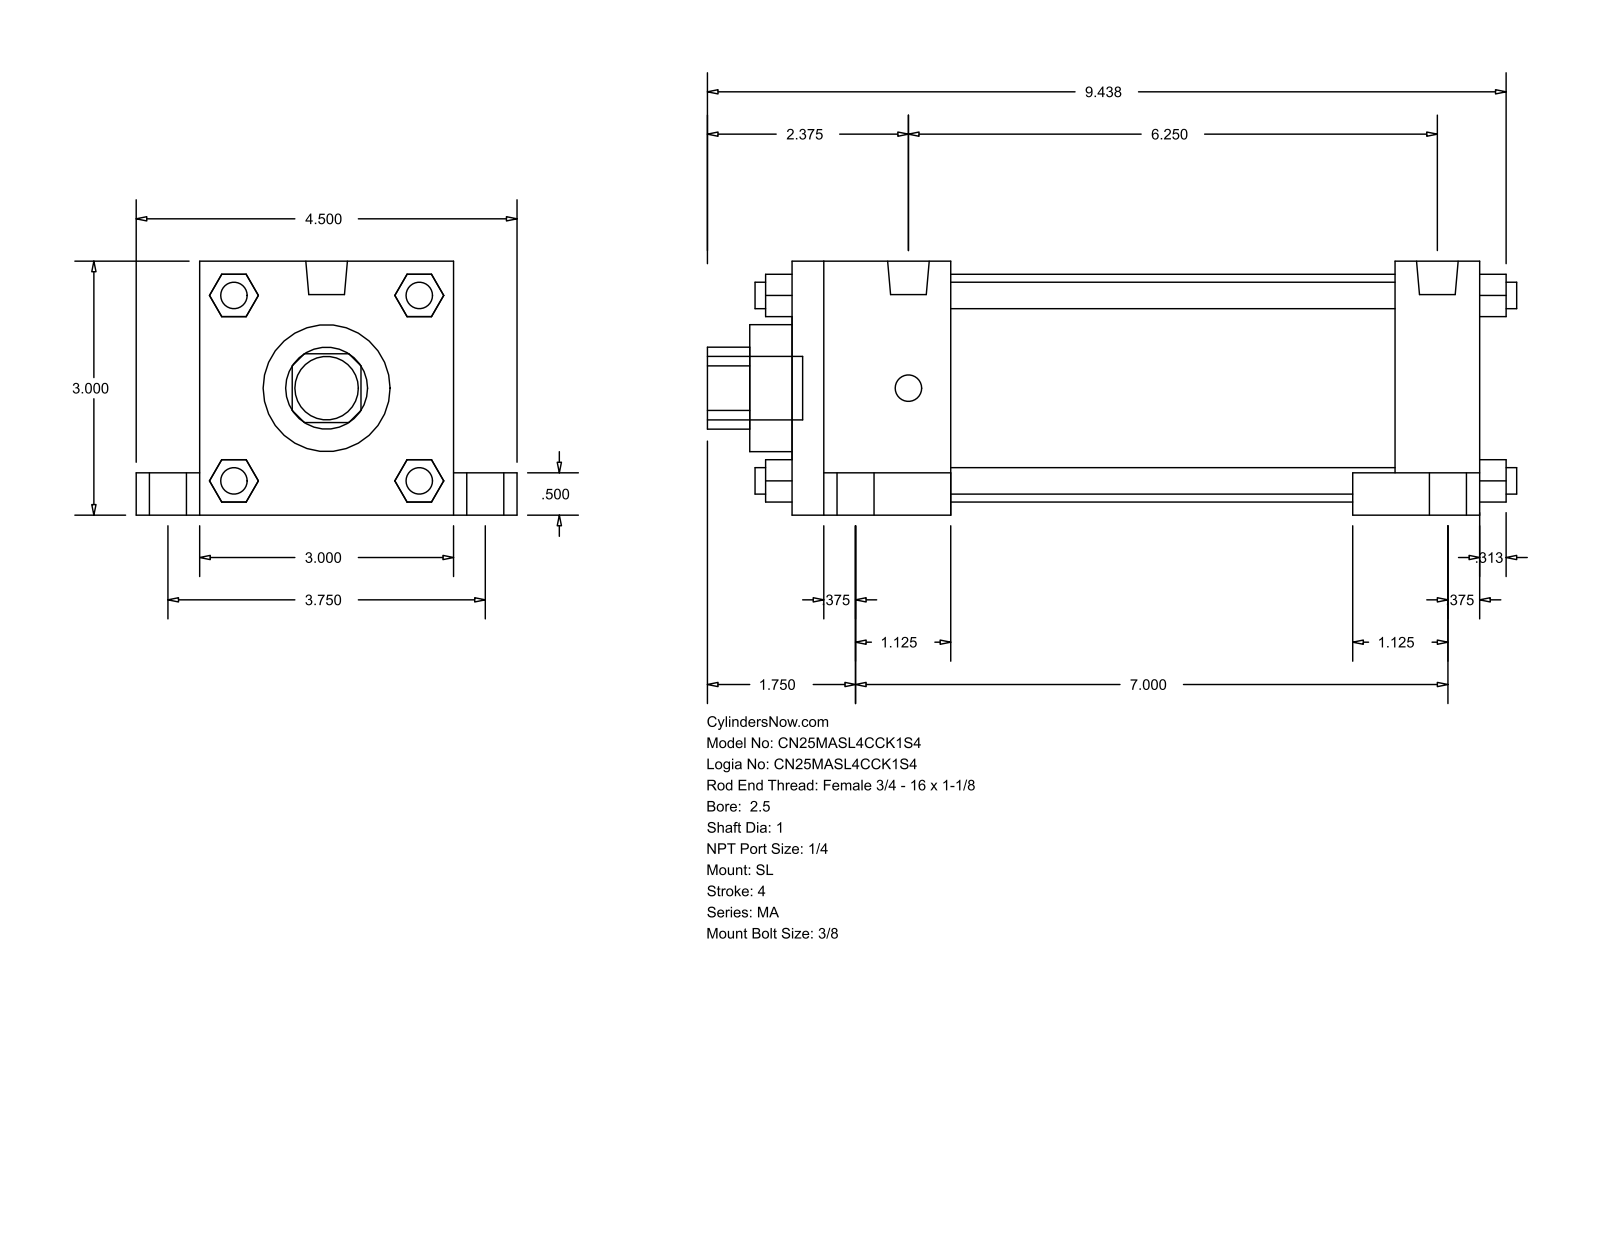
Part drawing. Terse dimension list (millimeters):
name: MA_SL__0250_1
written by: GSSL Pune (CONFIG_CONTROL_DESIGN)
unit: mm
bodies: 0 solids, 148 faces (112 planar, 36 cylindrical, 0 other)
size: 242.89 × 114.3 × 76.2
holes: 1× ⌀25.4, 1× ⌀38.1, 1× ⌀68.33
bosses: 8× ⌀7.94, 4× ⌀17.46, 4× ⌀11.11, 2× ⌀12.49, 1× ⌀19.05
rounds: 1× R12.29
face distances: 76.2, 206.38, 12.7, 133.35, 25.4, 47.63, 158.75, 180.98, 19.05, 95.25
